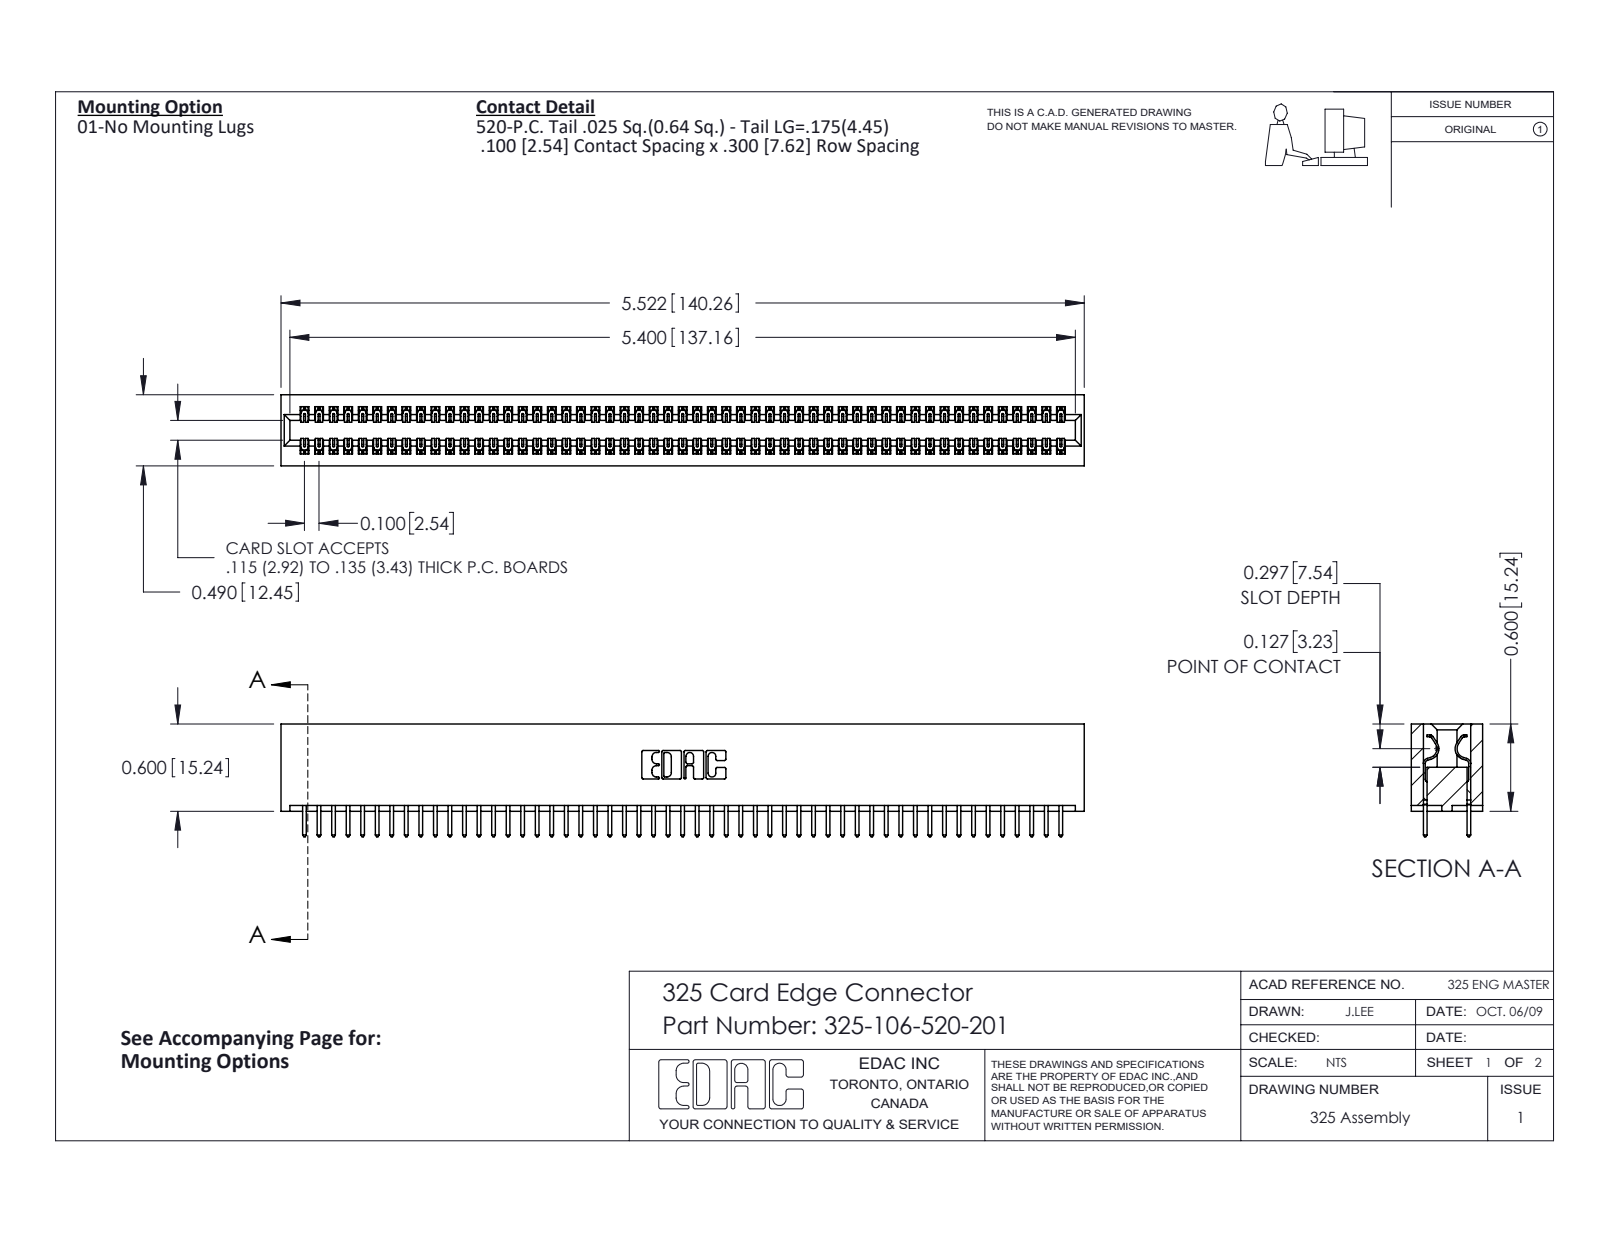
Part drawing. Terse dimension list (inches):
name: 325-106-520-201; 325 Part_Lugless; 325-292-001_325-293-120
written by: SolidWorks 2016 (CONFIG_CONTROL_DESIGN)
unit: in
bodies: 107 solids, 5618 faces (3882 planar, 1736 cylindrical, 0 other)
size: 5.522 × 0.775 × 0.49
volume: 1.147 in³; area: 36.36 in²
rounds: 159× R0.006, 106× R0.01, 22× R0.01, 6× R0.007, 6× R0.031, 3× R0.026, 2× R0.014, 2× R0.022
face distances: 0.083, 0.407, 0.3, 0.49, 0.107, 0.383, 0.025, 0.325, 0.275, 0.263
